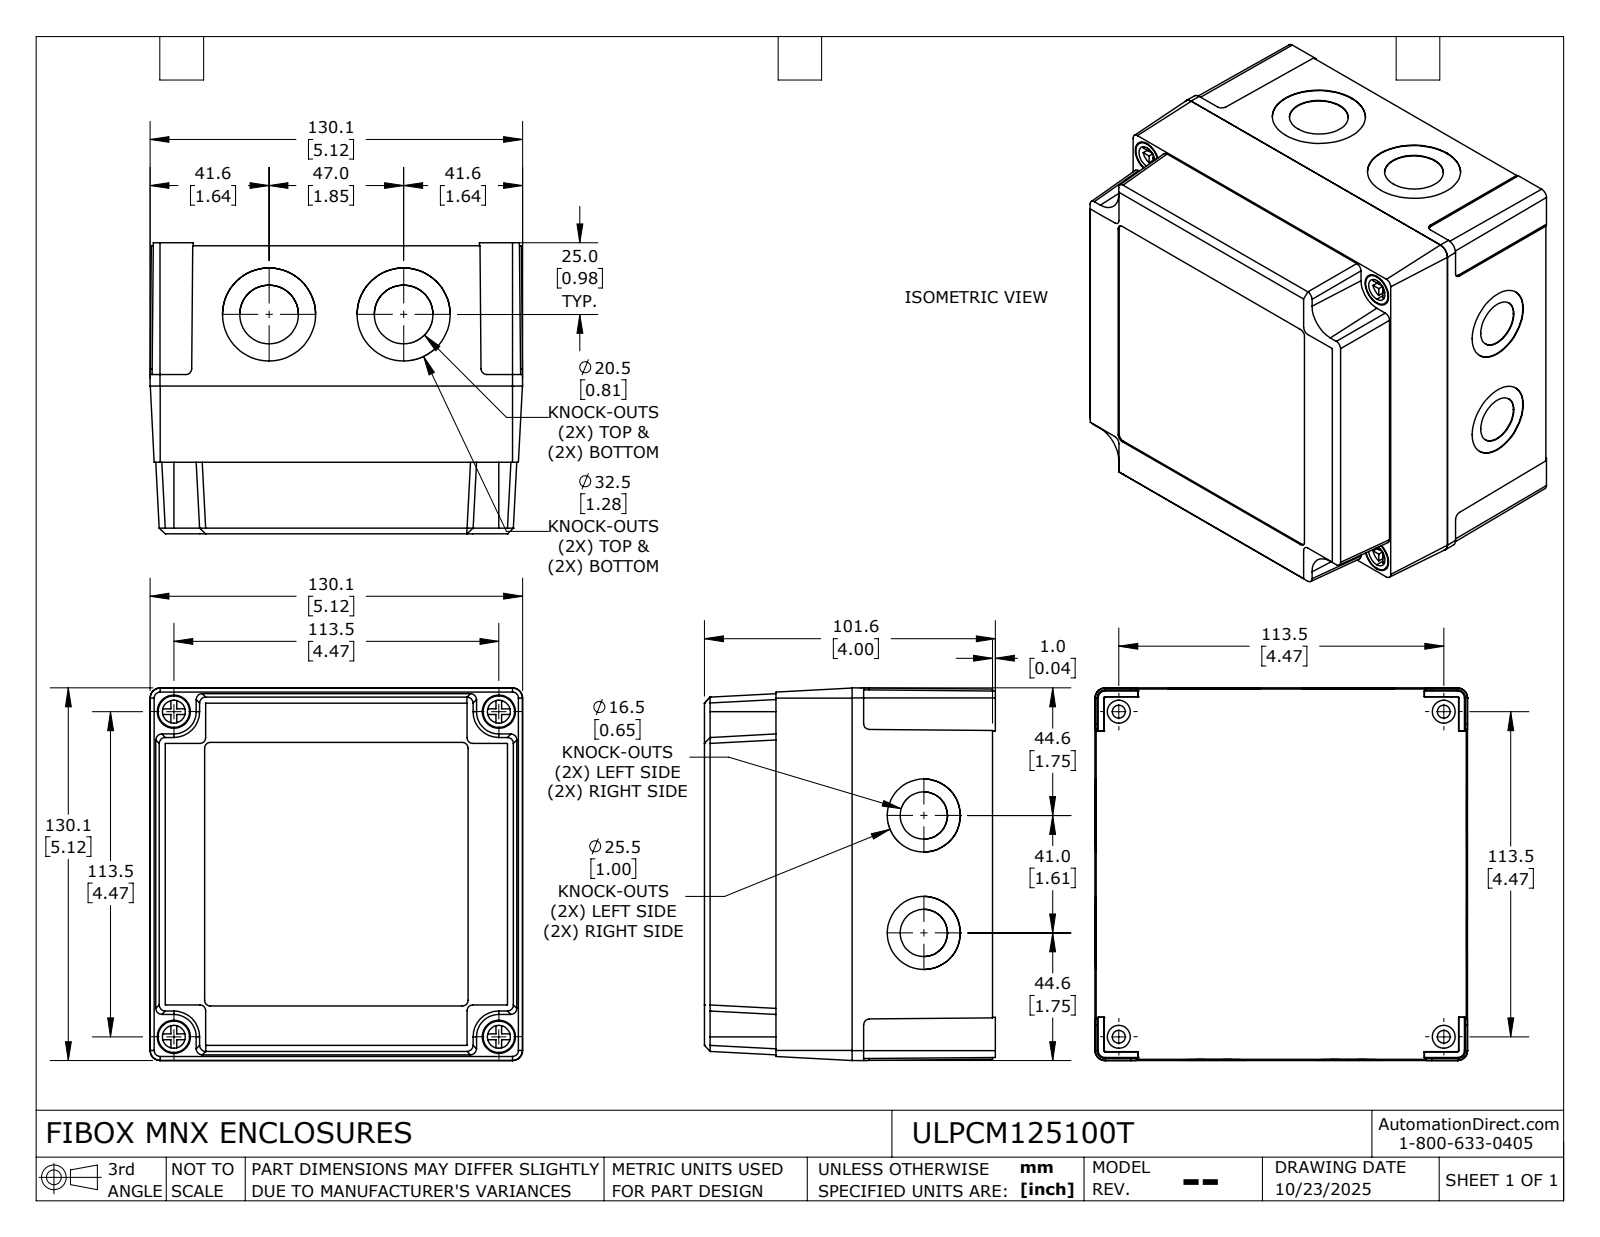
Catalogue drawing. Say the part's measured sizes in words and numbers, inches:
The part is named "ULPCM125100T_Default". Its 3-D file was written by "SolidWorks 2024 (CONFIG_CONTROL_DESIGN)". It is 6 solids with 569 faces: 331 planar, 192 cylindrical and 46 other. Overall it measures 5.122 by 5.122 by 4 inches. Its volume is 16.19 cubic inches and its surface area 274.1 square inches. Round holes: 8 of diameter 0.126, 8 of diameter 0.157, 4 of diameter 0.177, 4 of diameter 0.315, 4 of diameter 0.457, 4 of diameter 0.65, 4 of diameter 0.807, 4 of diameter 1.004, 4 of diameter 1.28. Round bosses or shafts: 8 of diameter 0.315, 8 of diameter 0.098, 4 of diameter 0.433, 4 of diameter 0.283. Partial cylindrical surfaces (rounded edges, fillets, slot ends): 8 of radius 0.079, 8 of radius 0.083, 6 of radius 0.056, 4 of radius 0.021, 4 of radius 0.197, 2 of radius 0.023. The main face-to-face distances are 0.165, 3.87, 0.118, 3.752, 0.078, 0.055, 0.022, 3.941, 3.823, 0.071. The hole center spacings are 2.281, 4.587, 0.888, 1.476, 1.796, 2.506, 3.543, 3.7.
